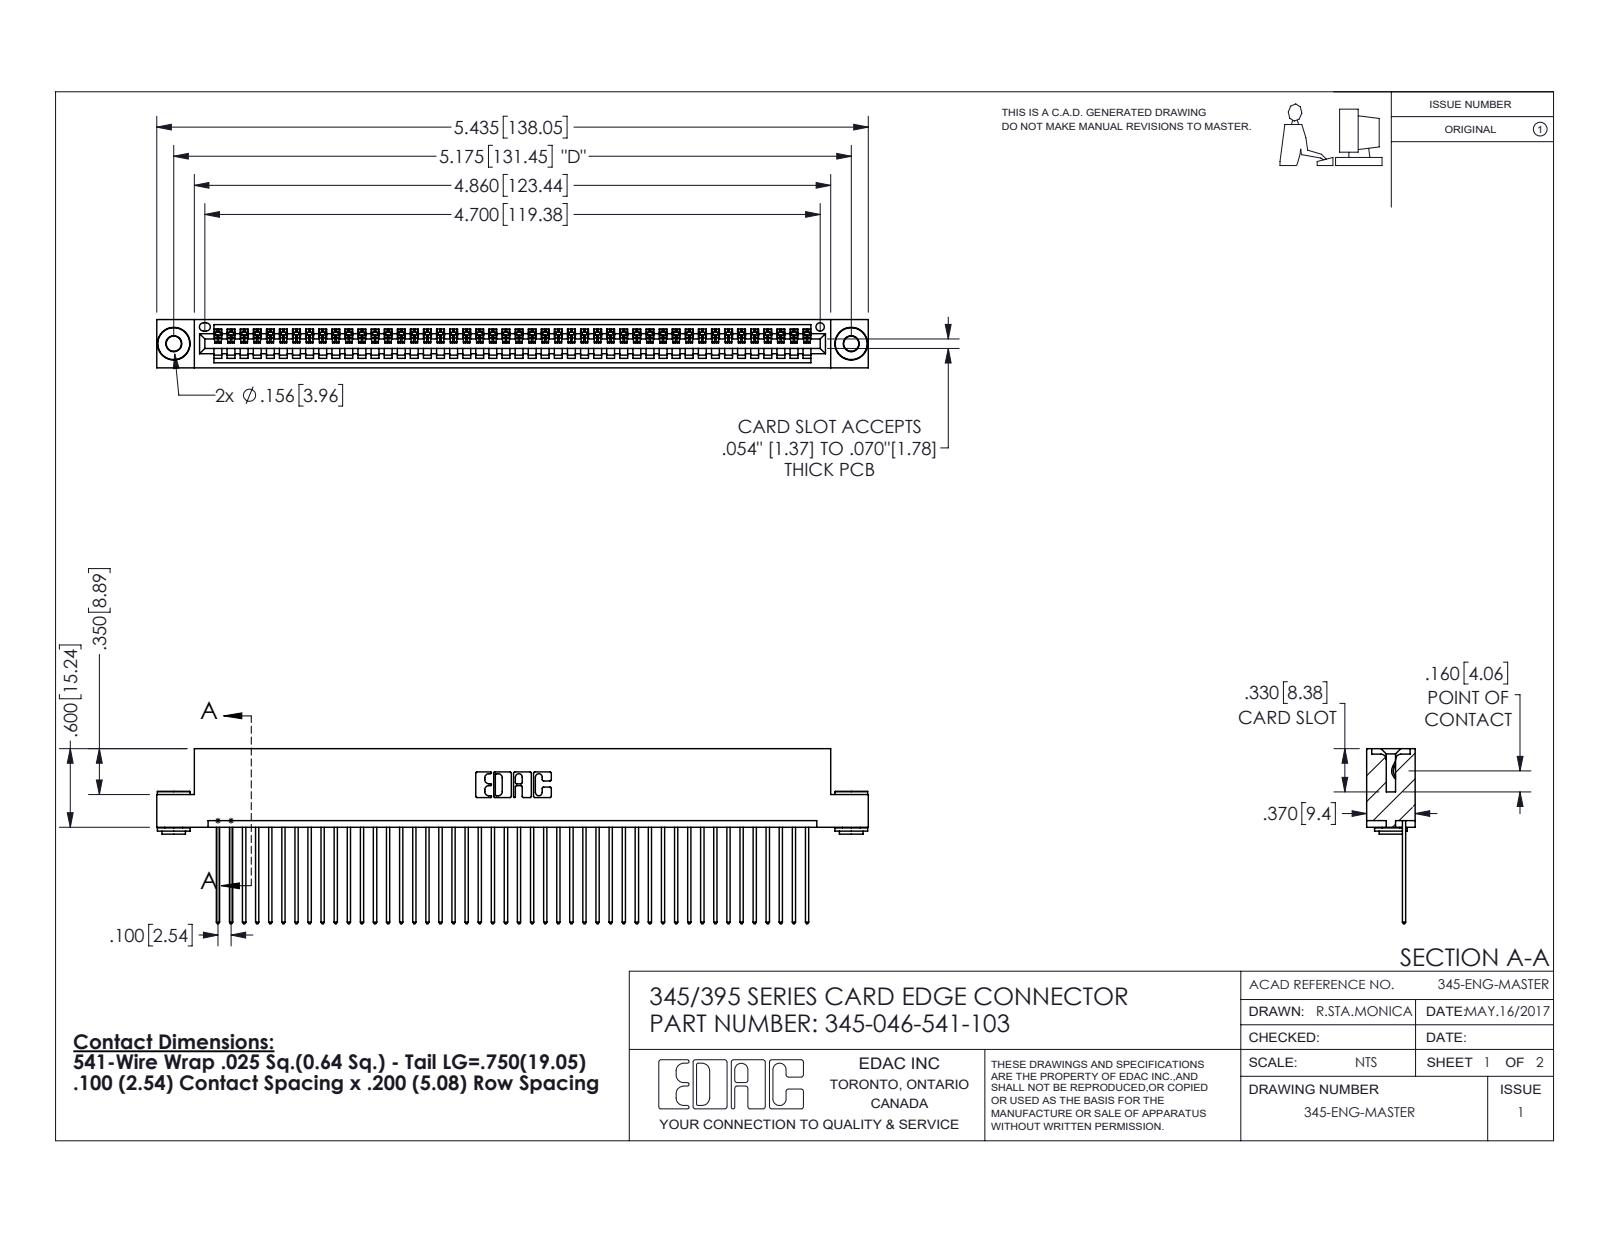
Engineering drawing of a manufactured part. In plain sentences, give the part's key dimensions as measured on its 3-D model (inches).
The part is named "345-250-002_345-250-002-102; 345 Part_Flush Mounting Lugs - 0.156 Dia-TH; 345-046-541-103; 345-292-001_345-293-141". Its 3-D file was written by "SolidWorks 2016 (CONFIG_CONTROL_DESIGN)". It is 49 solids with 2832 faces: 1930 planar, 894 cylindrical and 8 other. Overall it measures 5.435 by 1.337 by 0.37 inches. Its volume is 0.813 cubic inches and its surface area 29.23 square inches. Round holes: 2 of diameter 0.116, 2 of diameter 0.156, 1 of diameter 0.064. Round bosses or shafts: 2 of diameter 0.25, 2 of diameter 0.18, 2 of diameter 0.136. Partial cylindrical surfaces (rounded edges, fillets, slot ends): 92 of radius 0.006, 92 of radius 0.01, 22 of radius 0.01, 6 of radius 0.007, 6 of radius 0.031, 3 of radius 0.026, 2 of radius 0.031, 2 of radius 0.04. The main face-to-face distances are 0.072, 0.298, 0.025, 0.098, 0.272, 0.37, 0.2, 0.225, 0.149, 0.072. The hole center spacings are 0.27, 4.939, 5.175.
